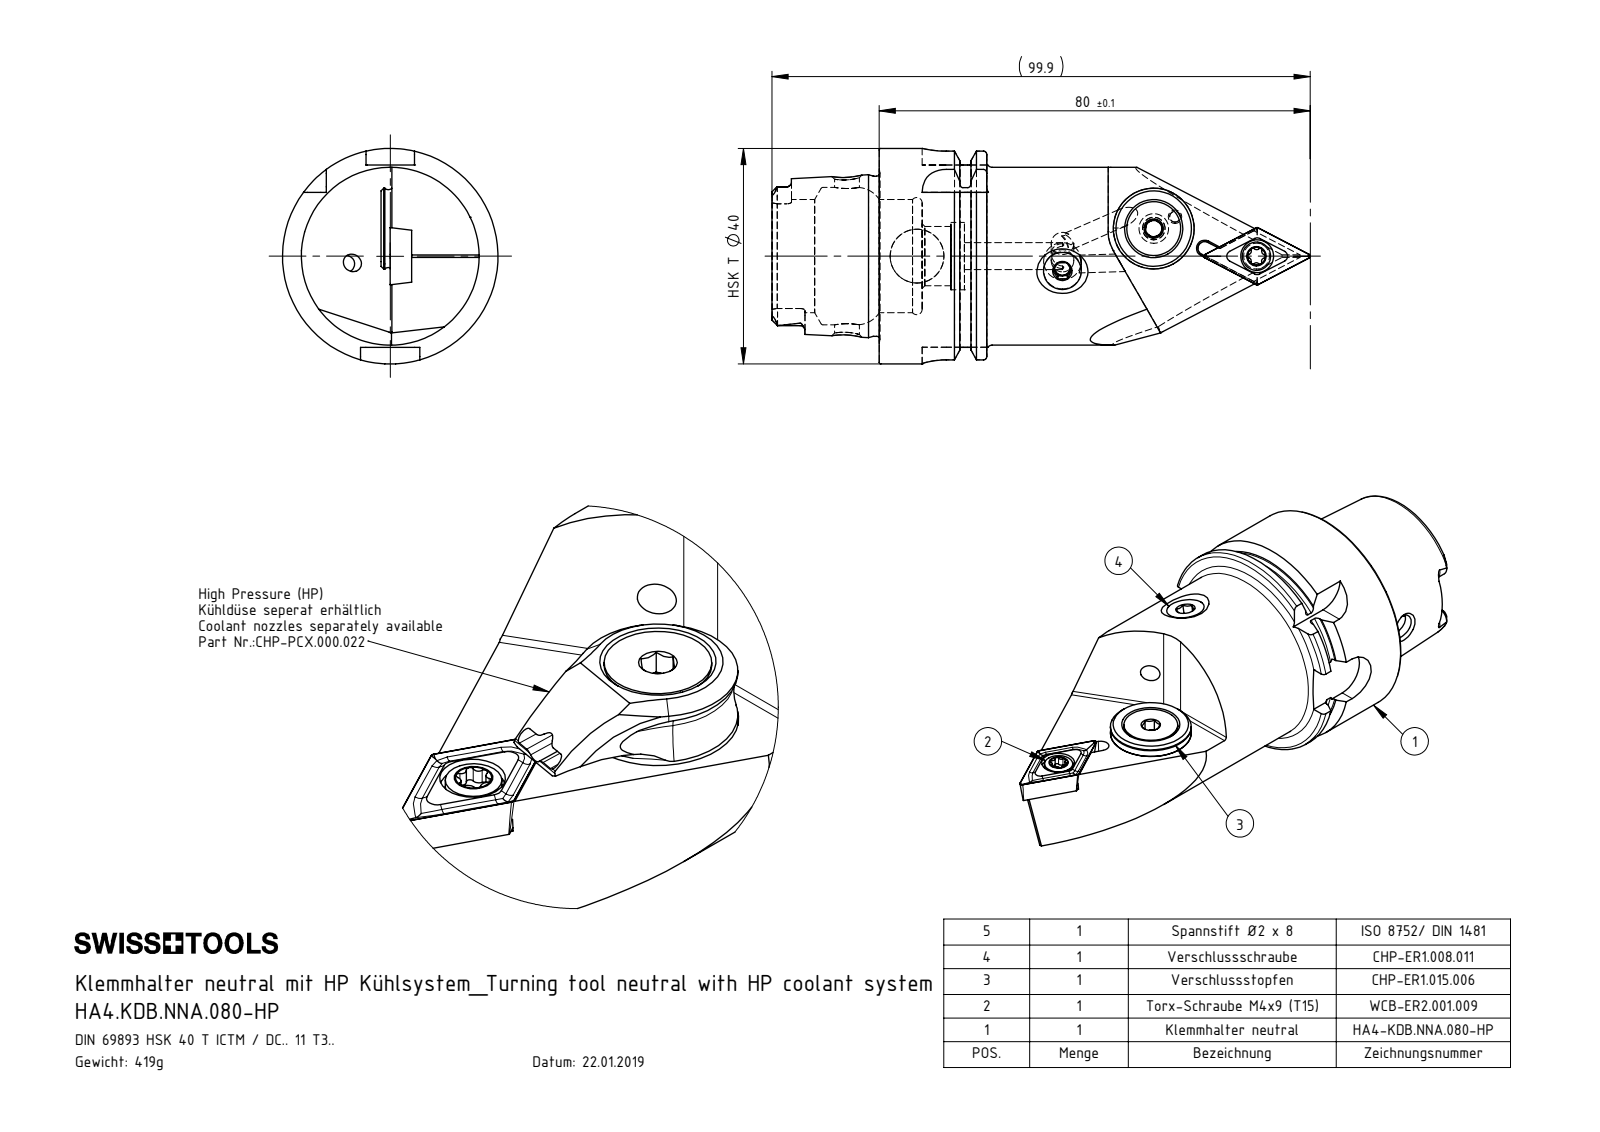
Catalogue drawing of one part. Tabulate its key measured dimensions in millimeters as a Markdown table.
| quantity | value |
| --- | --- |
| part name | CHP-ER1.015.006; ISO 8752 2x8; DIN 7991 - M5x15; CHP-ER1.015.006_A (+6 more) |
| STEP written by | SolidWorks 2017 (AUTOMOTIVE_DESIGN) |
| units | millimeters |
| bodies | 8 solids, 410 faces (116 planar, 117 cylindrical, 177 other) |
| overall size | 99.91 × 40 × 40 |
| volume | 52 955 mm³ |
| surface area | 17 399 mm² |
| round holes (diameter × count) | 3.3 × 3, 4.2 × 2, 1.2 × 1, 2 × 1, 2.5 × 1, 3 × 1, 4.4 × 1, 4.6 × 1, 5 × 1, 5.2 × 1, 6.1 × 1, 7 × 1 |
| round bosses / shafts (diameter × count) | 40 × 1, 34.75 × 1, 33 × 1, 29.71 × 1, 15 × 1, 13.4 × 1, 10 × 1, 8 × 1 |
| partial cylindrical surfaces (radius × count) | 0.34 × 6, 0.59 × 6, 0.9 × 6, 1.88 × 4, 4.5 × 4, 0.5 × 2, 1.25 × 1, 7 × 1 |
| main face-to-face distances | 4.5, 7.95, 12, 19.95, 0.83, 3.67, 42.5, 34.55, 22.55, 19.9 |
| hole center spacings | 4.49, 16.81, 16.93, 19.75, 19.87, 44.25, 48.43, 63.02 |
